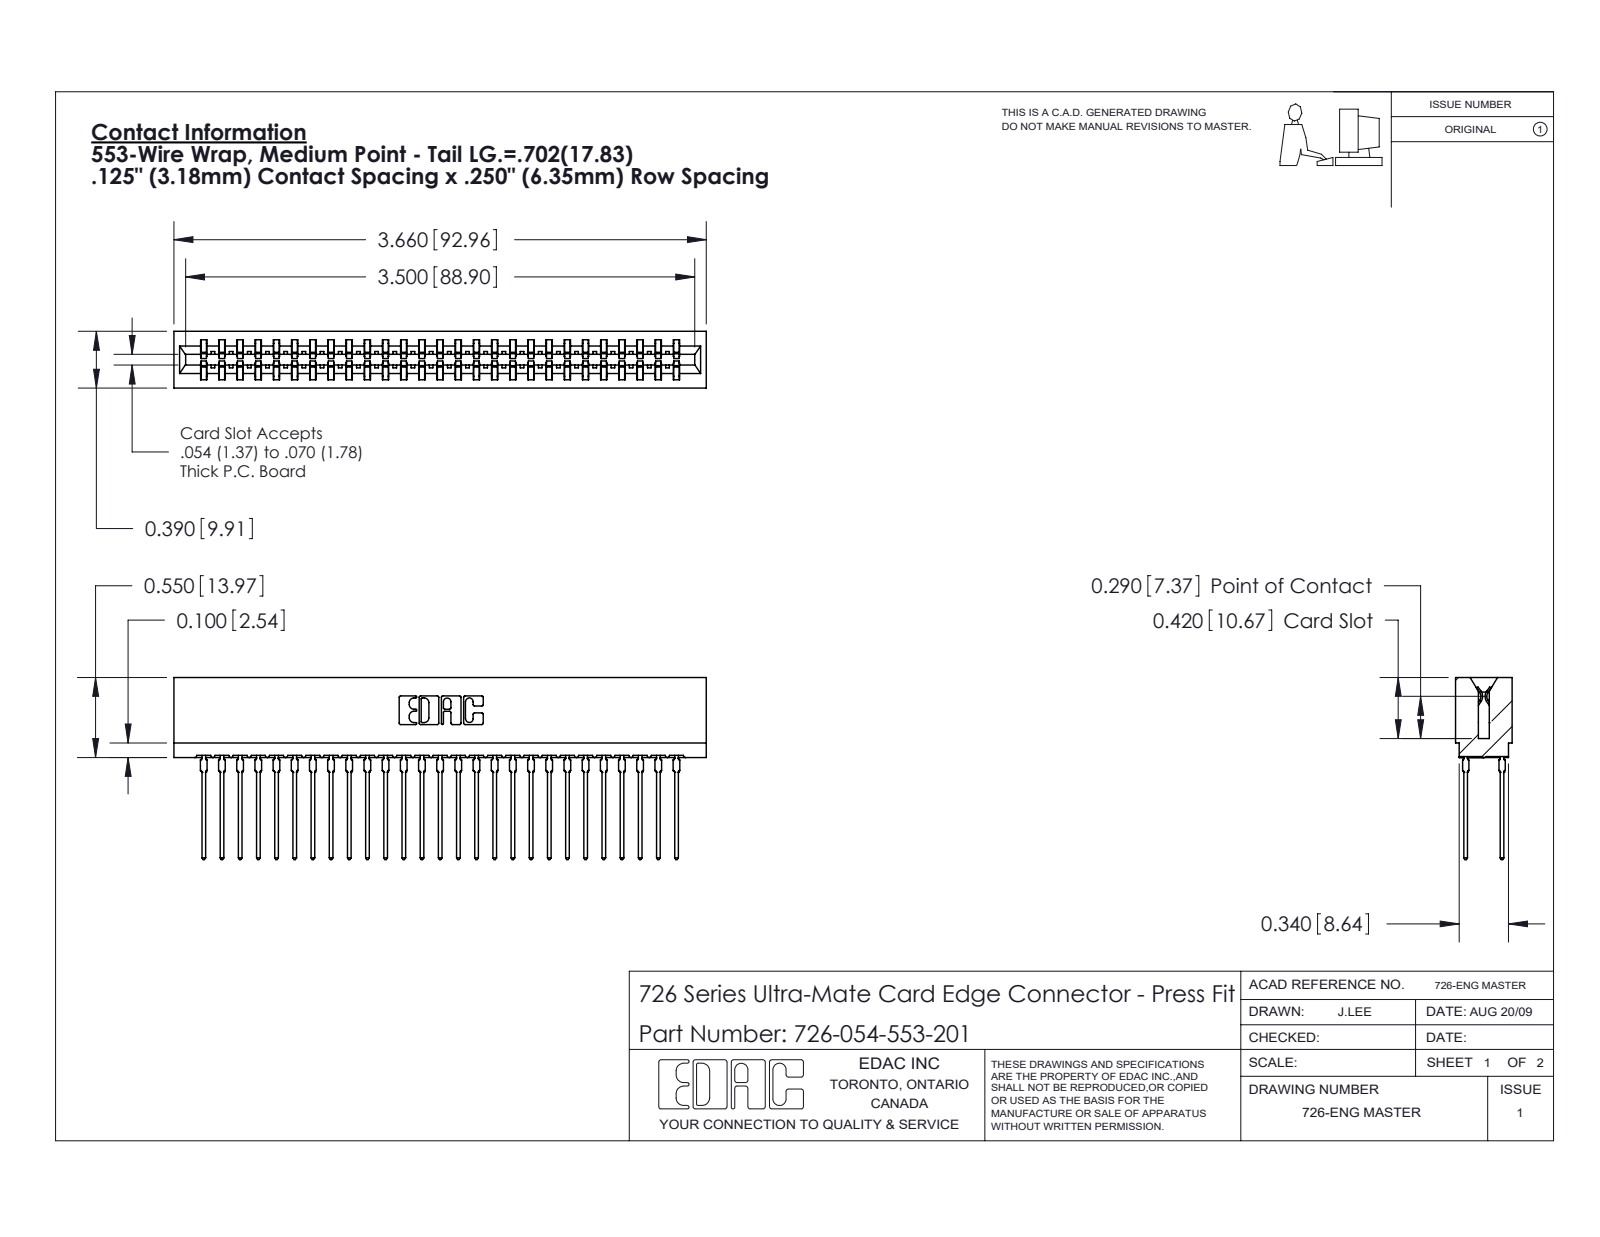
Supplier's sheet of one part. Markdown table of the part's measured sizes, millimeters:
| quantity | value |
| --- | --- |
| part name | 746-292-001_553; 726-054-553-201; 726 Part_.515 Slot Depth - 01 |
| STEP written by | SolidWorks 2020 (CONFIG_CONTROL_DESIGN) |
| units | millimeters |
| bodies | 55 solids, 4930 faces (2539 planar, 987 cylindrical, 1404 other) |
| overall size | 93 × 31.8 × 9.9 |
| volume | 8 880 mm³ |
| surface area | 15 620 mm² |
| partial cylindrical surfaces (radius × count) | 0.5 × 108, 0.4 × 28, 0.3 × 22, 0.1 × 8, 0.3 × 8, 0.2 × 6, 0.8 × 6, 0.7 × 3 |
| main face-to-face distances | 1.4, 8.5, 6.4, 0.6, 7.8, 2.1, 9.9, 7, 12.7, 5.7 |
